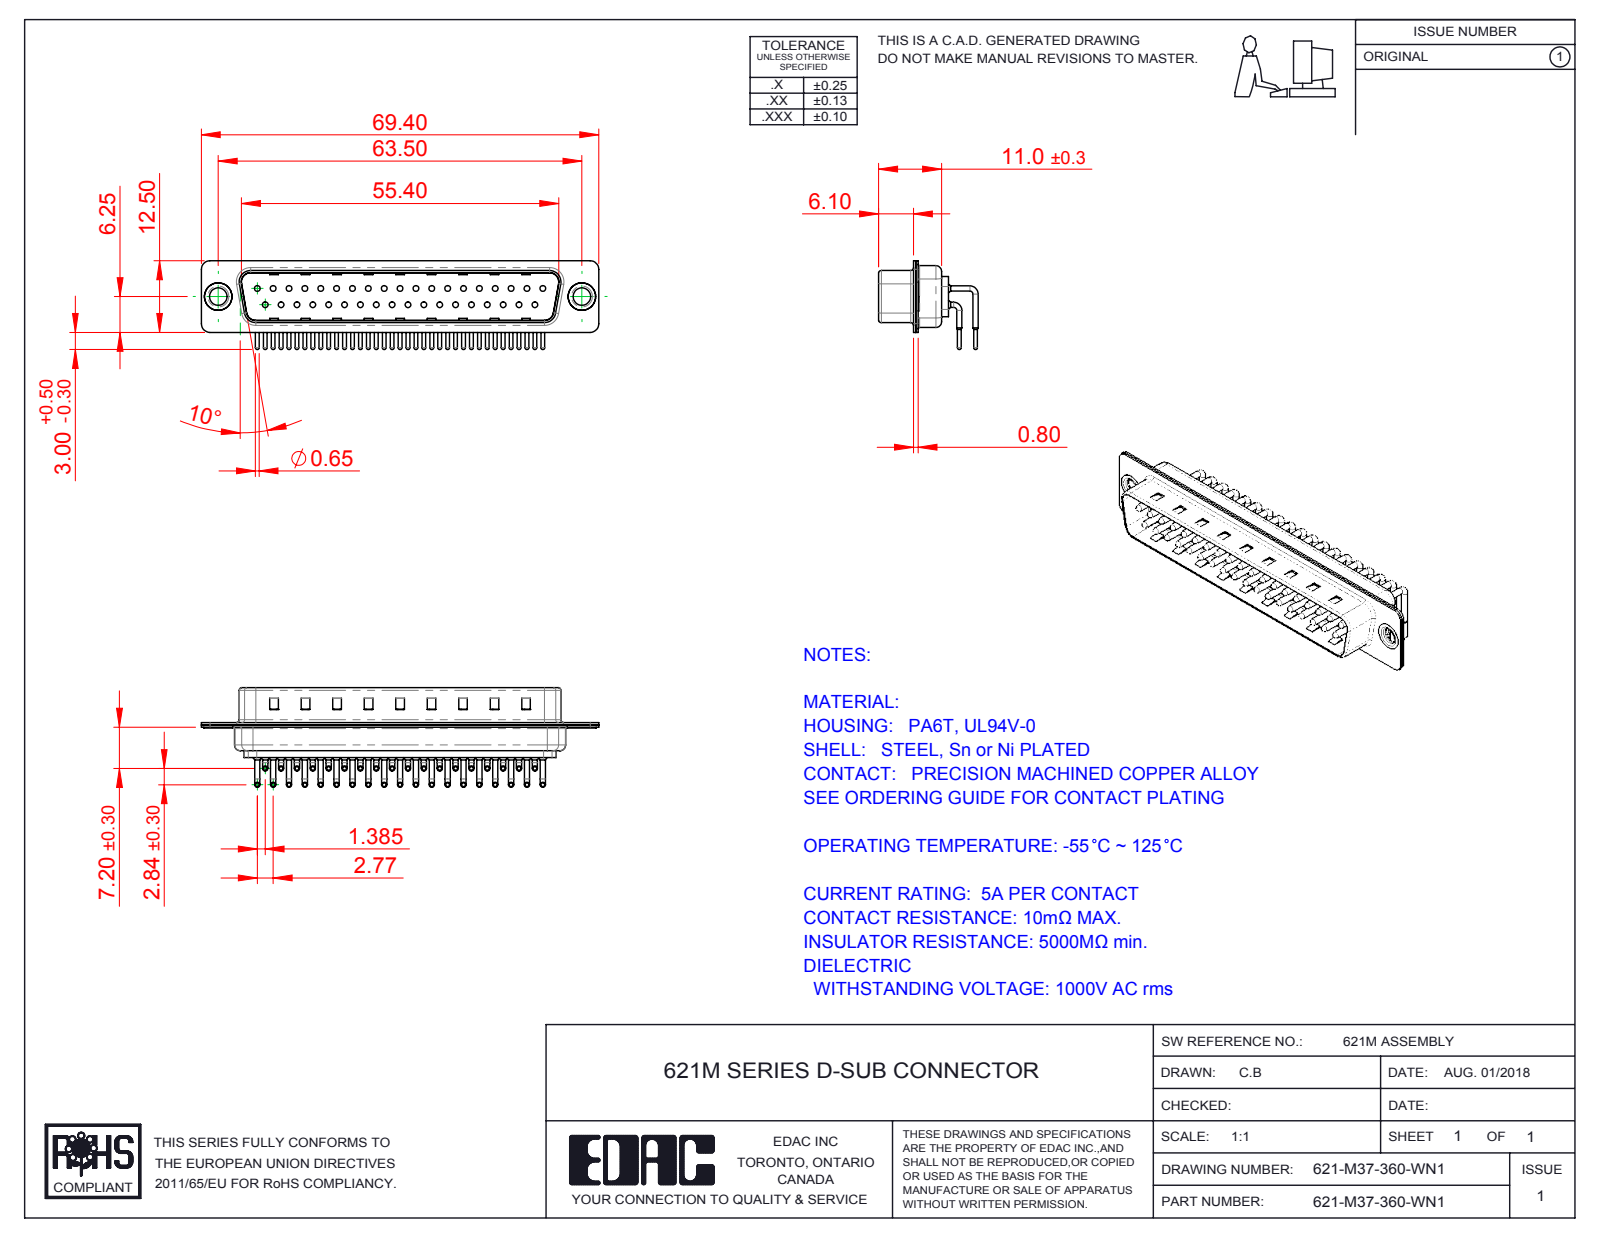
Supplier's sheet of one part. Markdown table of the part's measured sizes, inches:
| quantity | value |
| --- | --- |
| part name | 621M Housing_37 Contacts; 621M Contact Row 1; 621M Contact Row 2; 621M Shell Front_37 Contacts (+3 more) |
| STEP written by | SolidWorks 2016 (CONFIG_CONTROL_DESIGN) |
| units | inches |
| bodies | 42 solids, 4456 faces (2571 planar, 1457 cylindrical, 428 other) |
| overall size | 2.732 × 0.685 × 0.61 |
| volume | 0.239 in³ |
| surface area | 15.84 in² |
| round holes (diameter × count) | 0.039 × 37, 0.067 × 37, 0.079 × 37, 0.12 × 2, 0.157 × 2, 0.189 × 2 |
| round bosses / shafts (diameter × count) | 0.035 × 74, 0.059 × 37, 0.026 × 37, 0.197 × 2, 0.193 × 2, 0.14 × 2 |
| partial cylindrical surfaces (radius × count) | 0.04 × 37, 0.059 × 16, 0.079 × 12, 0.02 × 8, 0.063 × 8, 0.01 × 4, 0.024 × 4, 0.026 × 4 |
| main face-to-face distances | 0.016, 0.033, 0.376, 0.343, 0.049, 0.409, 0.059, 0.075, 0.014, 0.392 |
| hole center spacings | 0.124, 0.109, 0.218, 0.327, 0.198, 0.398, 0.436, 0.503 |
